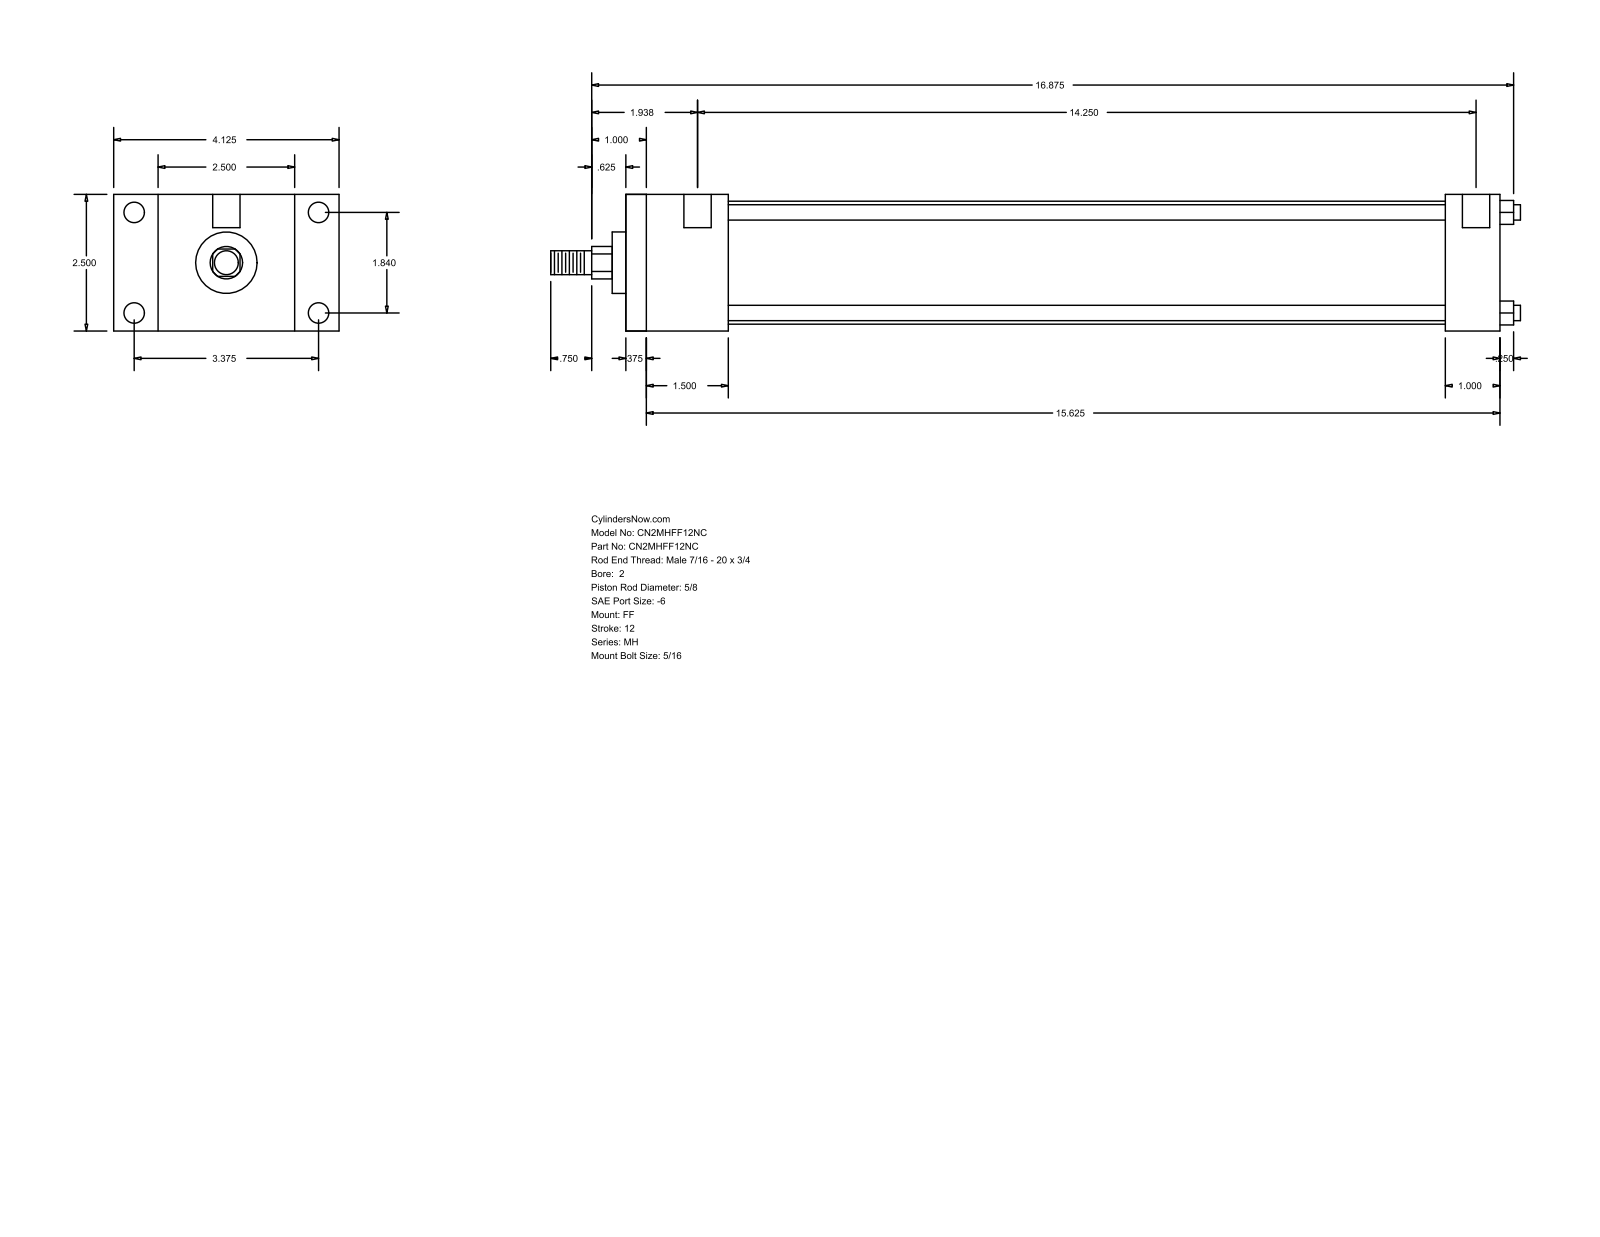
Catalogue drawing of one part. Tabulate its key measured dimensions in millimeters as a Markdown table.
| quantity | value |
| --- | --- |
| part name | MH_FF__0200_0.625 |
| STEP written by | GSSL Pune (CONFIG_CONTROL_DESIGN) |
| units | millimeters |
| bodies | 0 solids, 92 faces (64 planar, 28 cylindrical, 0 other) |
| overall size | 450.85 × 104.78 × 63.5 |
| round holes (diameter × count) | 5.56 × 4, 9.53 × 4, 12.7 × 2 |
| round bosses / shafts (diameter × count) | 7.14 × 4, 57.15 × 1, 28.57 × 1, 15.88 × 1, 11.11 × 1 |
| partial cylindrical surfaces (radius × count) | 7.54 × 1 |
| main face-to-face distances | 63.5, 406.39, 9.52, 396.87, 38.1, 47.62, 381, 371.48, 333.38, 358.77 |
| hole center spacings | 46.74, 85.72, 97.63, 369.89, 3.18, 4.76, 361.95, 365.13 |
